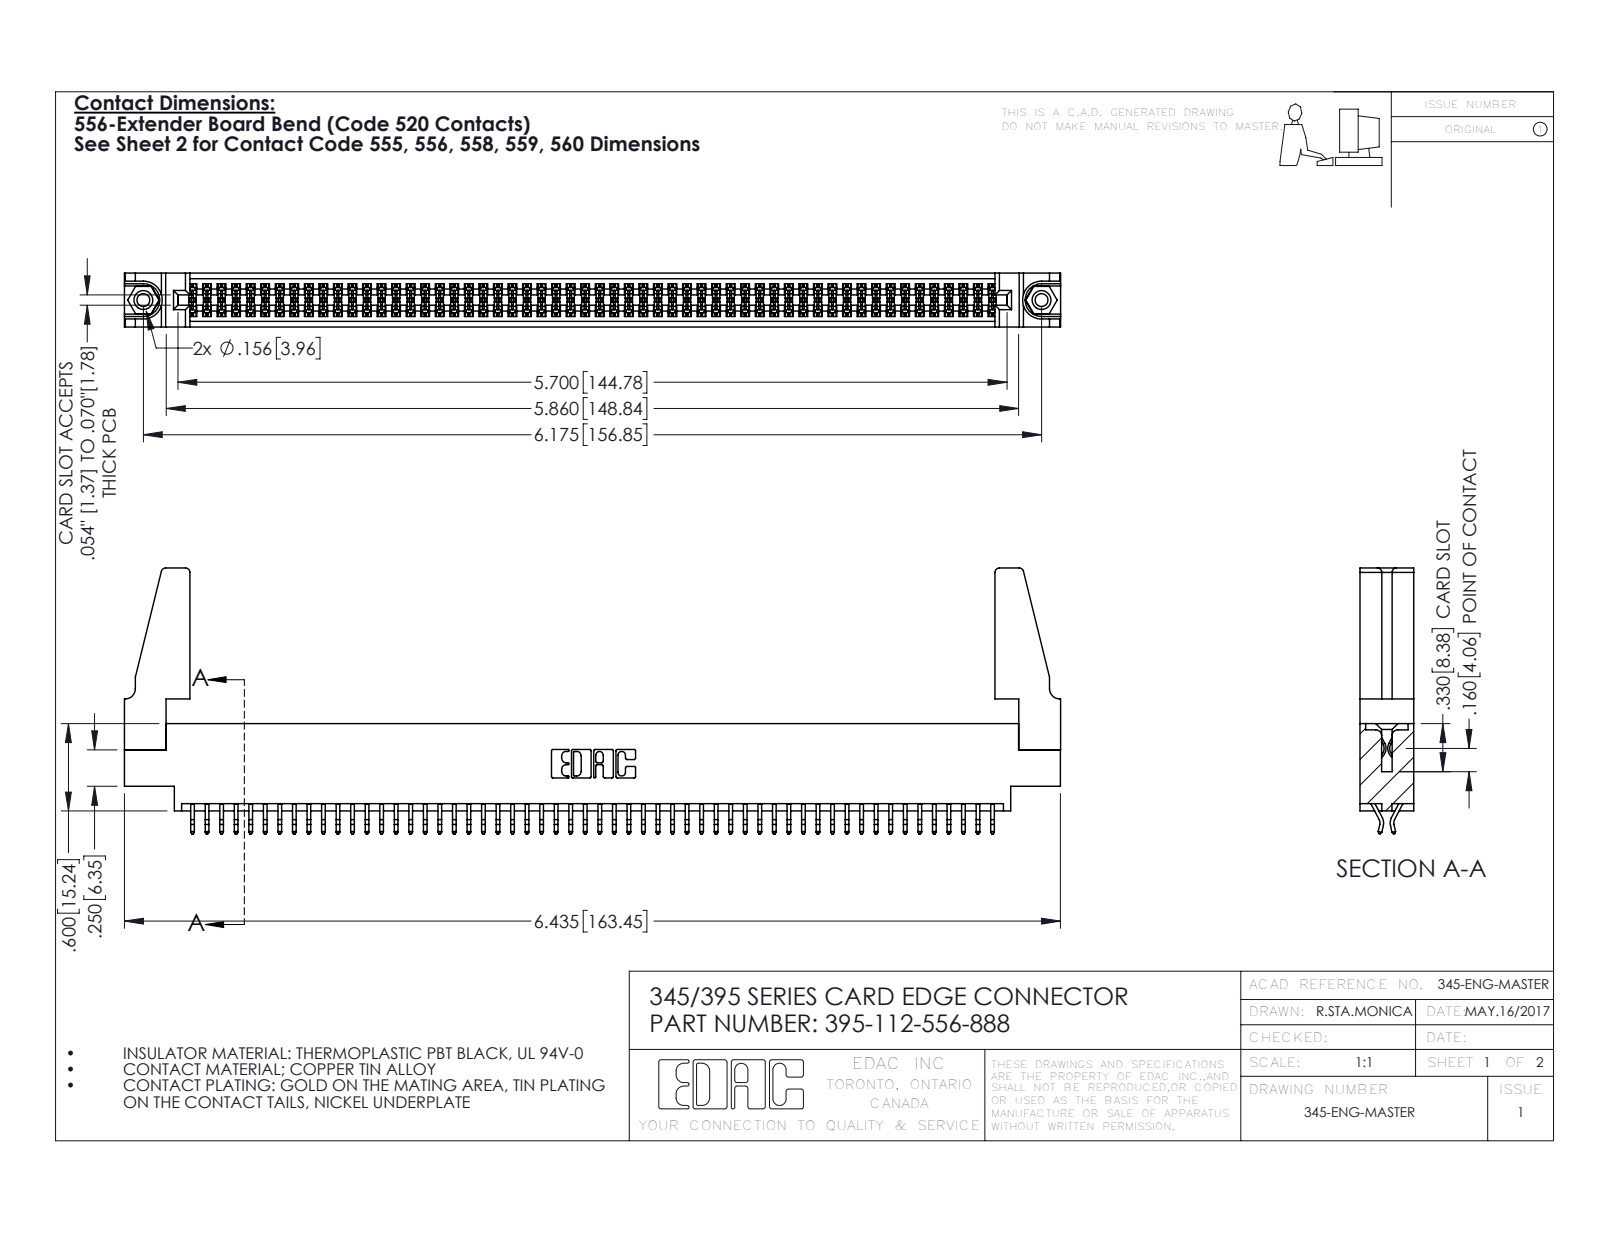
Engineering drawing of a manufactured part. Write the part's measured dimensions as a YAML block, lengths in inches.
part_name: "345-250-001_345-250-001-102; 395-112-556-888; 345-292-001_556 Tail; 345-220-078_345-220-088 (+1 more)"
step_written_by: "SolidWorks 2016 (CONFIG_CONTROL_DESIGN)"
units: inches
bodies: {solids: 117, faces: 6526, planar: 4300, cylindrical: 2210, other: 16}
overall_size: [6.436, 1.827, 0.37]
volume: 1.168
surface_area: 41.74
round_holes:
  - {diameter: 0.089, count: 2}
  - {diameter: 0.125, count: 2}
  - {diameter: 0.156, count: 2}
  - {diameter: 0.064, count: 1}
round_bosses_or_shafts:
  - {diameter: 0.155, count: 2}
partial_cylinders:
  - {radius: 0.006, count: 168}
  - {radius: 0.01, count: 22}
  - {radius: 0.03, count: 8}
  - {radius: 0.007, count: 6}
  - {radius: 0.031, count: 6}
  - {radius: 0.026, count: 3}
  - {radius: 0.01, count: 2}
  - {radius: 0.014, count: 2}
face_to_face_distances: [0.072, 0.298, 0.37, 0.025, 0.2, 0.098, 0.272, 0.225, 0.175, 0.149]
hole_center_spacings: [0.27, 5.939, 6.175]
